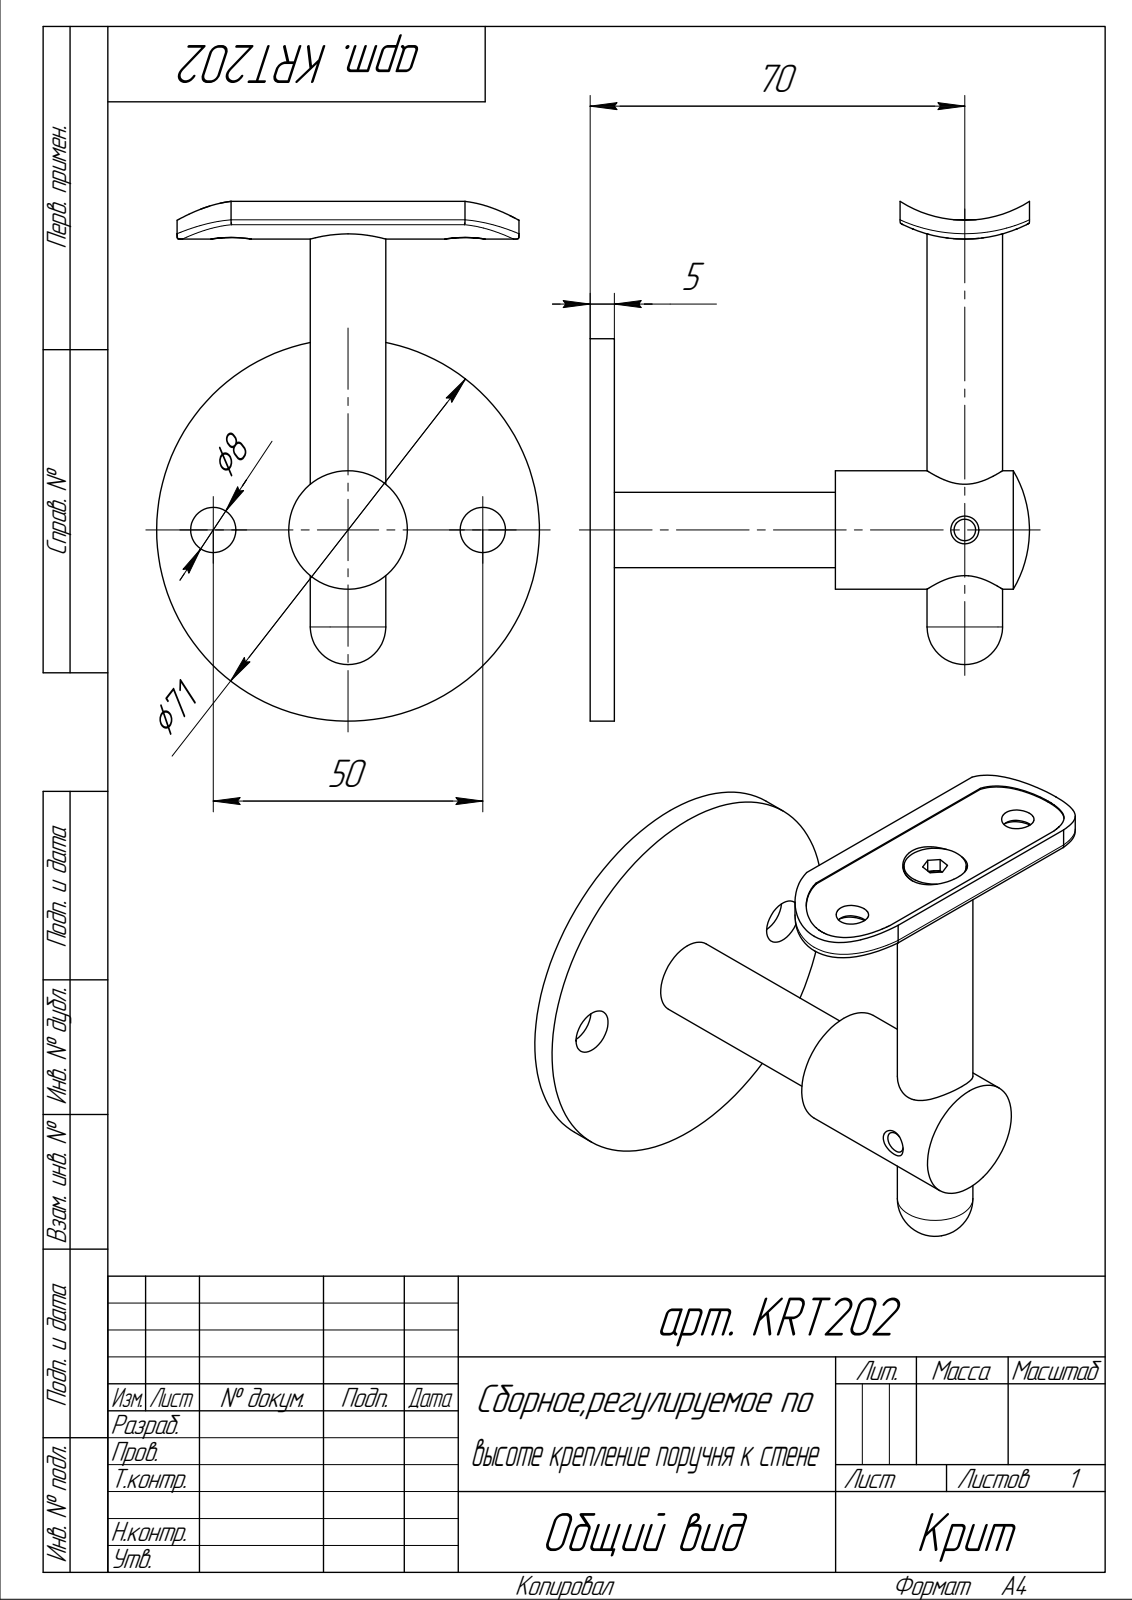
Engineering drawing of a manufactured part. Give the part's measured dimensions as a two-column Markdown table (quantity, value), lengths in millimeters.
| quantity | value |
| --- | --- |
| part name | Сборка; Деталь; арт. KRT201.003; socket countersunk head screw_din_DIN 7991 - M6 x 16 --- 9.7N |
| STEP written by | ASCON Math Kernel (AUTOMOTIVE_DESIGN) |
| units | millimeters |
| bodies | 4 solids, 78 faces (28 planar, 27 cylindrical, 23 other) |
| overall size | 96.5 × 81.5 × 71 |
| volume | 49 711 mm³ |
| surface area | 22 059 mm² |
| round holes (diameter × count) | 6 × 2, 8.4 × 2, 4 × 1, 5 × 1, 12 × 1, 14 × 1 |
| round bosses / shafts (diameter × count) | 71 × 1, 22 × 1, 14 × 1, 11.57 × 1, 6 × 1 |
| partial cylindrical surfaces (radius × count) | 12.2 × 2, 4.5 × 1, 22.32 × 1, 22.52 × 1, 23.52 × 1, 25.82 × 1 |
| main face-to-face distances | 4.5, 45.5, 41, 81.5, 77, 36, 57.5, 53, 12, 24 |
| hole center spacings | 21.7, 43.4, 50 |
